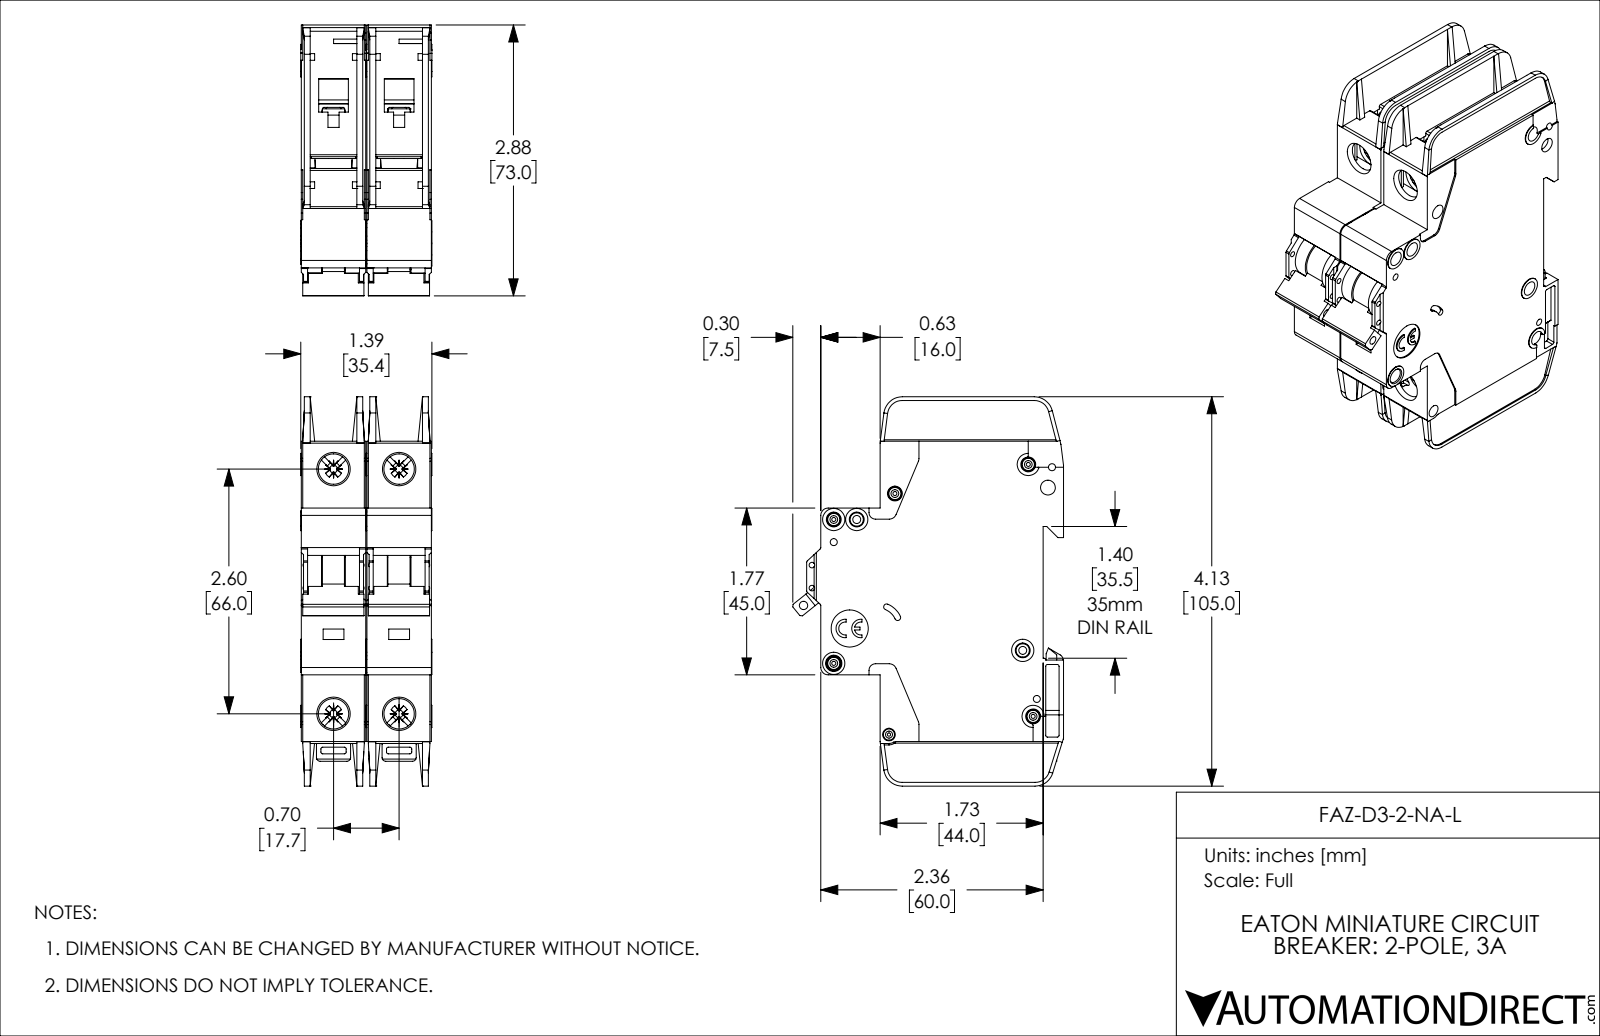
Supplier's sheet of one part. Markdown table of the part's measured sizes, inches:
| quantity | value |
| --- | --- |
| part name | FAZ-D3-2-NA-L |
| STEP written by | SolidWorks 2019 (AUTOMOTIVE_DESIGN) |
| units | inches |
| bodies | 2 solids, 2254 faces (1342 planar, 714 cylindrical, 198 other) |
| overall size | 4.134 × 2.876 × 1.394 |
| volume | 9.365 in³ |
| surface area | 82.01 in² |
| round holes (diameter × count) | 0.157 × 8, 0.043 × 5, 0.075 × 4, 0.323 × 4, 0.059 × 2, 0.085 × 2, 0.035 × 1, 0.089 × 1, 0.098 × 1, 0.134 × 1, 0.394 × 1 |
| round bosses / shafts (diameter × count) | 0.13 × 5, 0.236 × 4, 0.118 × 3, 0.098 × 2 |
| partial cylindrical surfaces (radius × count) | 0.02 × 57, 0.016 × 20, 0.039 × 14, 0.079 × 10, 0.043 × 8, 0.008 × 5, 0.197 × 5, 0.01 × 4 |
| main face-to-face distances | 0.697, 0.047, 0.685, 0.591, 0.094, 0.638, 0.543, 1.382, 0.744, 0.65 |
| hole center spacings | 0.244, 0.537, 0.697, 0.87, 2.598, 2.69, 0.189, 0.199 |
